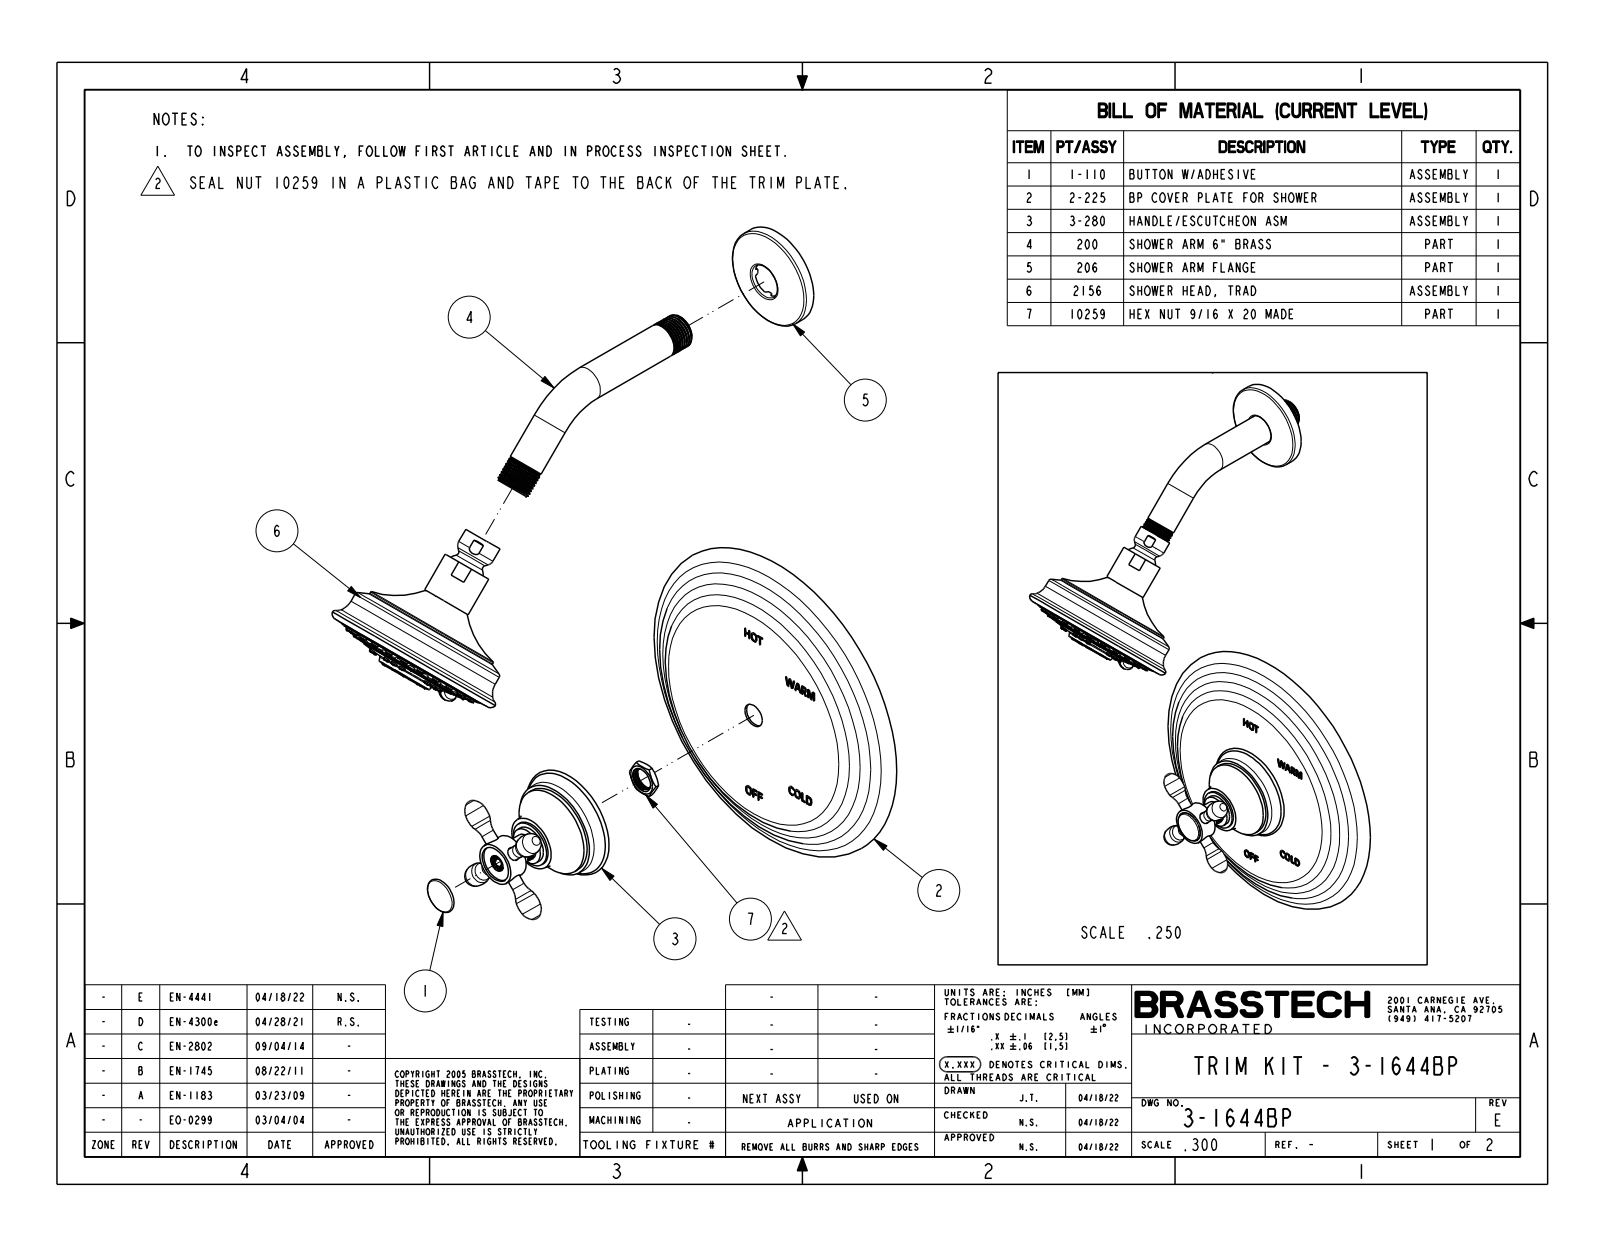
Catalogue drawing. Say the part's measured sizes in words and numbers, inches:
The part is named "3-1644BP". Its 3-D file was written by "CREO PARAMETRIC BY PTC INC, 2018400 (CONFIG_CONTROL_DESIGN)". It is 2 solids with 1361 faces: 264 planar, 222 cylindrical and 875 other. Overall it measures 17.065 by 8.25 by 7.75 inches. Its volume is 52.45 cubic inches and its surface area 192.5 square inches. Round holes: 8 of diameter 0.059, 2 of diameter 0.313, 1 of diameter 0.85, 1 of diameter 0.925. Round bosses or shafts: 39 of diameter 0.142, 23 of diameter 0.165, 2 of diameter 0.813, 2 of diameter 0.3, 1 of diameter 3.81, 1 of diameter 3.724, 1 of diameter 3.24, 1 of diameter 2.38. Partial cylindrical surfaces (rounded edges, fillets, slot ends): 8 of radius 0.079, 2 of radius 0.02, 1 of radius 0.138, 1 of radius 0.472, 1 of radius 0.512, 1 of radius 0.63. The main face-to-face distances are 0.754, 0.063, 0.118, 0.181, 1.229, 0.475, 0.9, 2.129, 1.375, 1.979. The hole center spacings are 0.443, 0.579, 0.818, 0.819, 1.069, 0.443, 0.578, 1.069.
